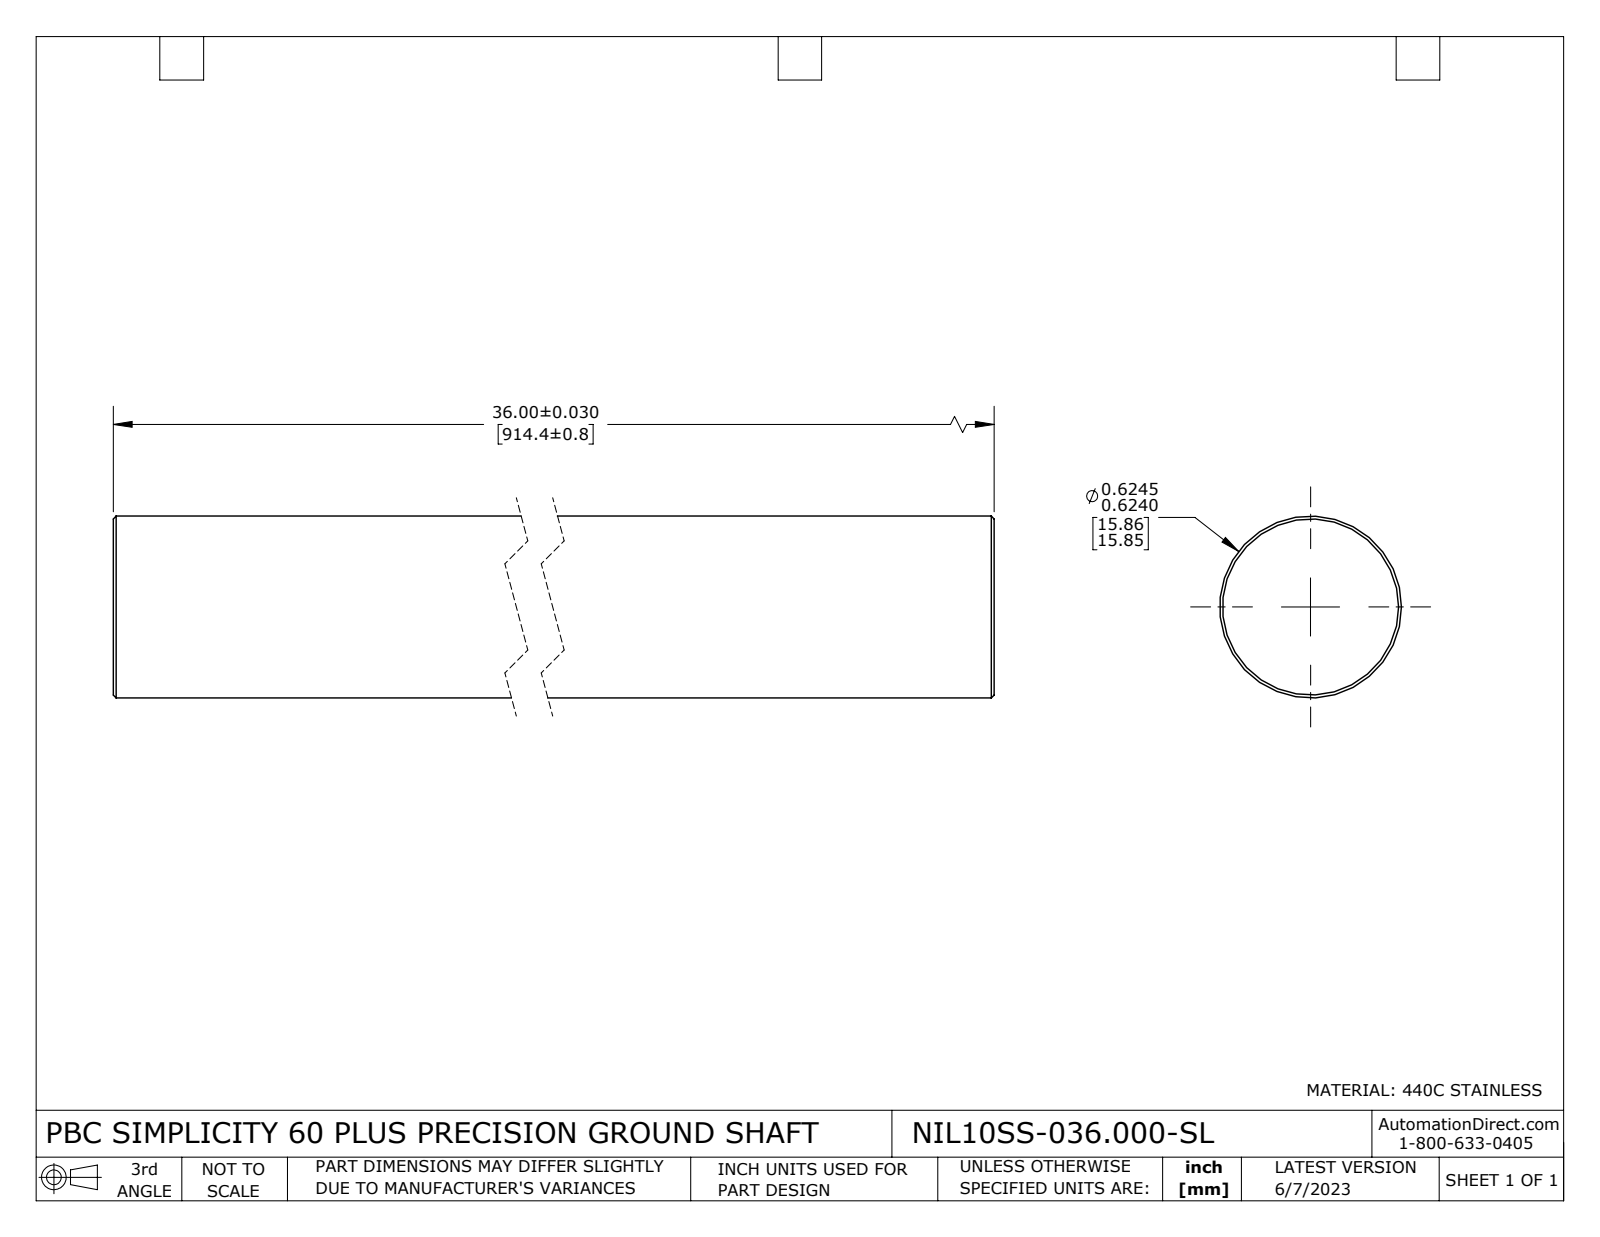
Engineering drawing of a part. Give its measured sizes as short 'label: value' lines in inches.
name: NIL10SS-036.000-SL
written by: SolidWorks 2021 (CONFIG_CONTROL_DESIGN)
unit: in
bodies: 1 solid, 8 faces (2 planar, 2 cylindrical, 4 other)
size: 36 × 0.625 × 0.625
volume: 11.04 in³; area: 71.28 in²
bosses: 1× ⌀0.625
face distances: 36
